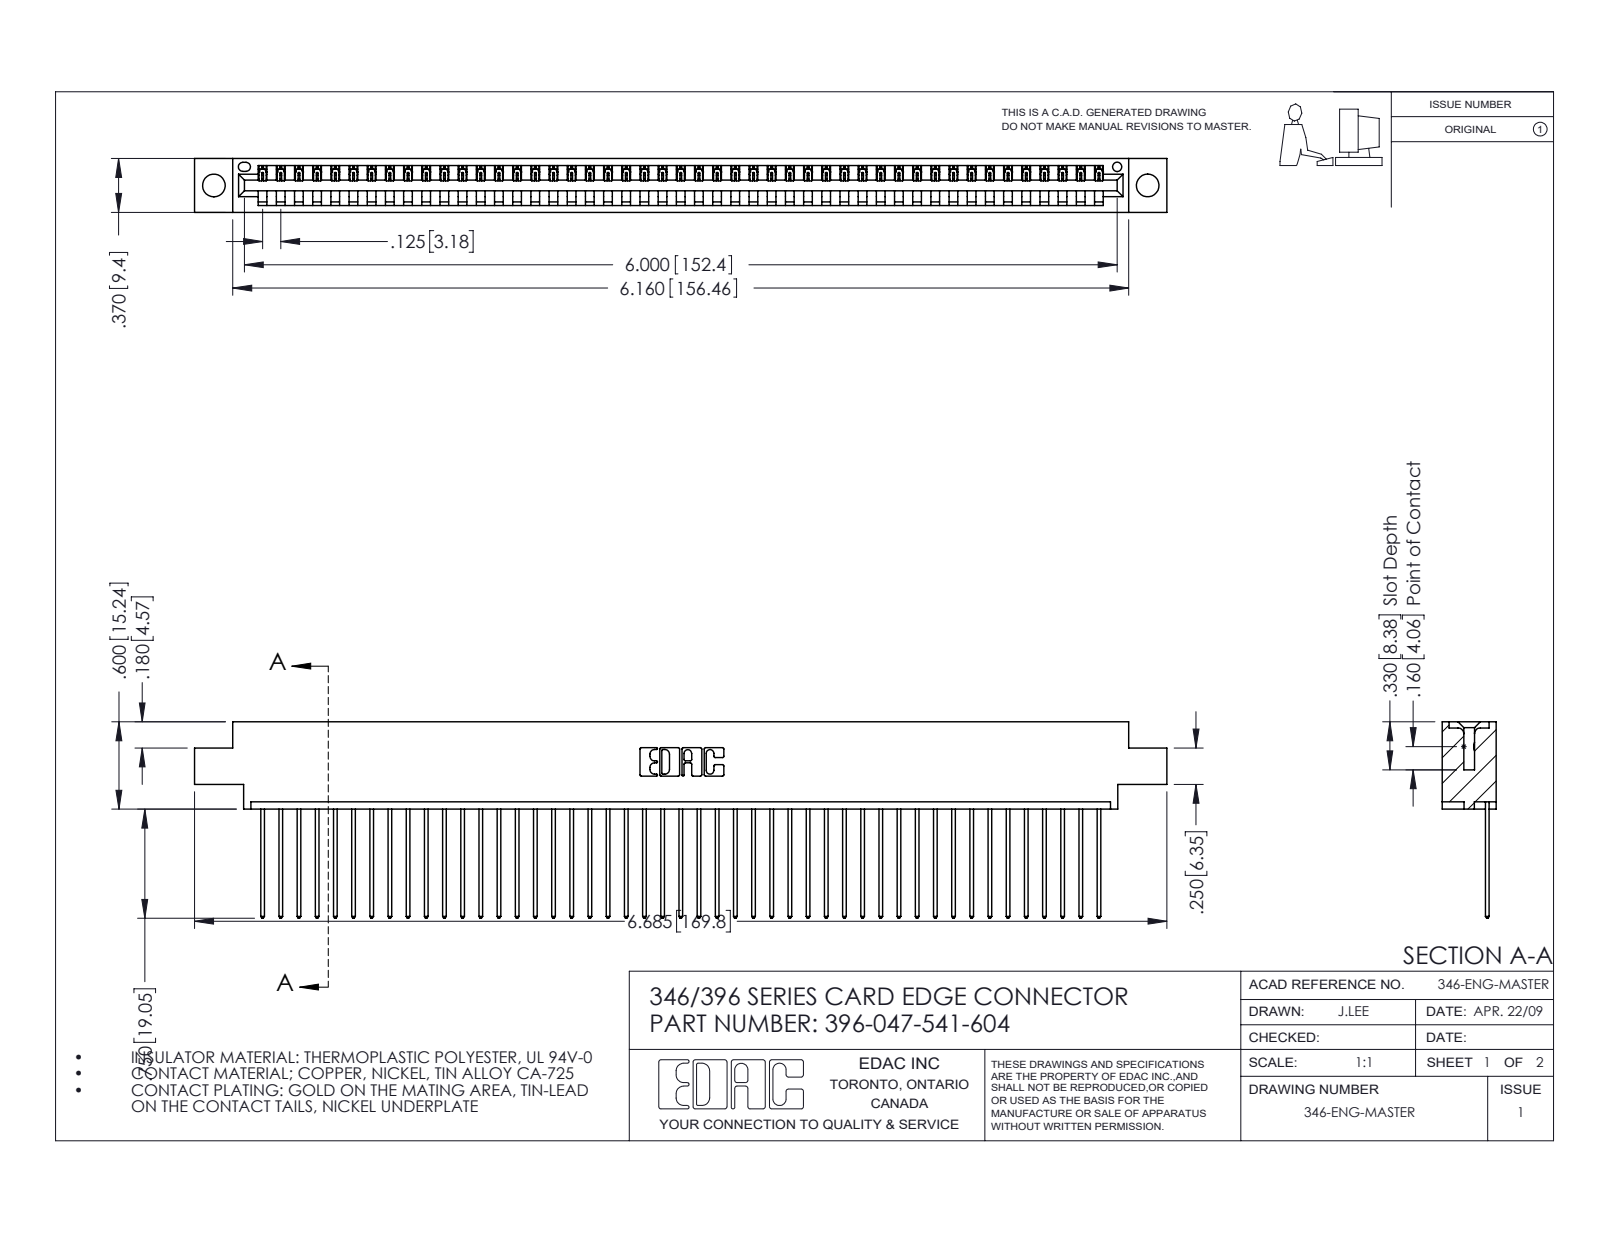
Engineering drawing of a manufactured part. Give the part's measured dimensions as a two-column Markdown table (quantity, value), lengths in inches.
| quantity | value |
| --- | --- |
| part name | 346 Part_0.170 Offset - 0.156 Dia-TH; 345-292-001_345-293-141; 396-047-541-604 |
| STEP written by | SolidWorks 2016 (CONFIG_CONTROL_DESIGN) |
| units | inches |
| bodies | 48 solids, 2852 faces (1960 planar, 892 cylindrical, 0 other) |
| overall size | 6.685 × 1.35 × 0.37 |
| volume | 0.989 in³ |
| surface area | 32.85 in² |
| round holes (diameter × count) | 0.156 × 2, 0.064 × 1 |
| partial cylindrical surfaces (radius × count) | 0.006 × 94, 0.01 × 94, 0.01 × 22, 0.007 × 6, 0.031 × 6, 0.026 × 3, 0.031 × 2, 0.04 × 2 |
| main face-to-face distances | 0.048, 0.322, 0.37, 0.25, 0.072, 0.298, 0.025, 0.148, 0.222, 0.1 |
| hole center spacings | 0.246, 6.211, 6.42 |
